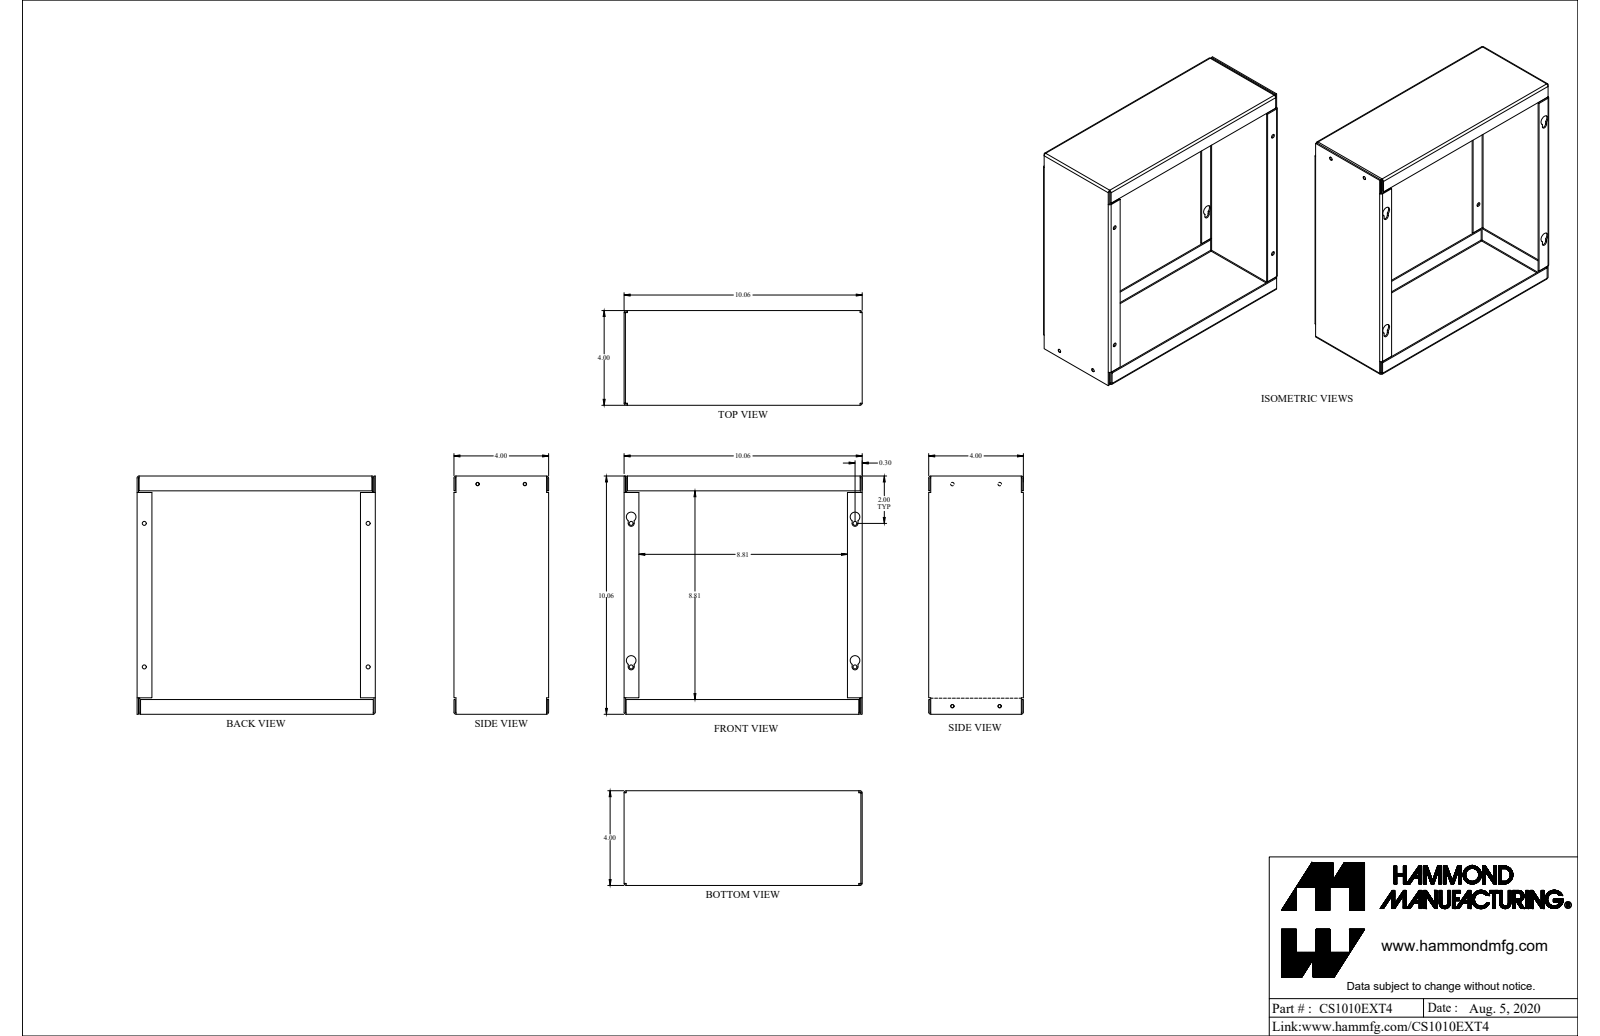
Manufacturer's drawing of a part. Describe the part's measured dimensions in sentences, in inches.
The part is named "CS1010EXT4". Its 3-D file was written by "SolidWorks 2021 (AUTOMOTIVE_DESIGN)". It is 2 solids with 124 faces: 80 planar, 44 cylindrical and 0 other. Overall it measures 10.063 by 10.063 by 4 inches. Its volume is 11.59 cubic inches and its surface area 413.5 square inches. Round holes: 4 of diameter 0.145, 4 of diameter 0.17. Round bosses or shafts: 4 of diameter 0.131. Partial cylindrical surfaces (rounded edges, fillets, slot ends): 12 of radius 0.029, 12 of radius 0.086, 4 of radius 0.125, 4 of radius 0.203. The main face-to-face distances are 10.006, 0.057, 0.057, 9.948, 3.943, 10.063, 10.062, 9.949, 3.886, 4. The hole center spacings are 2, 6.062, 9.38, 9.459, 9.591, 11.235.
